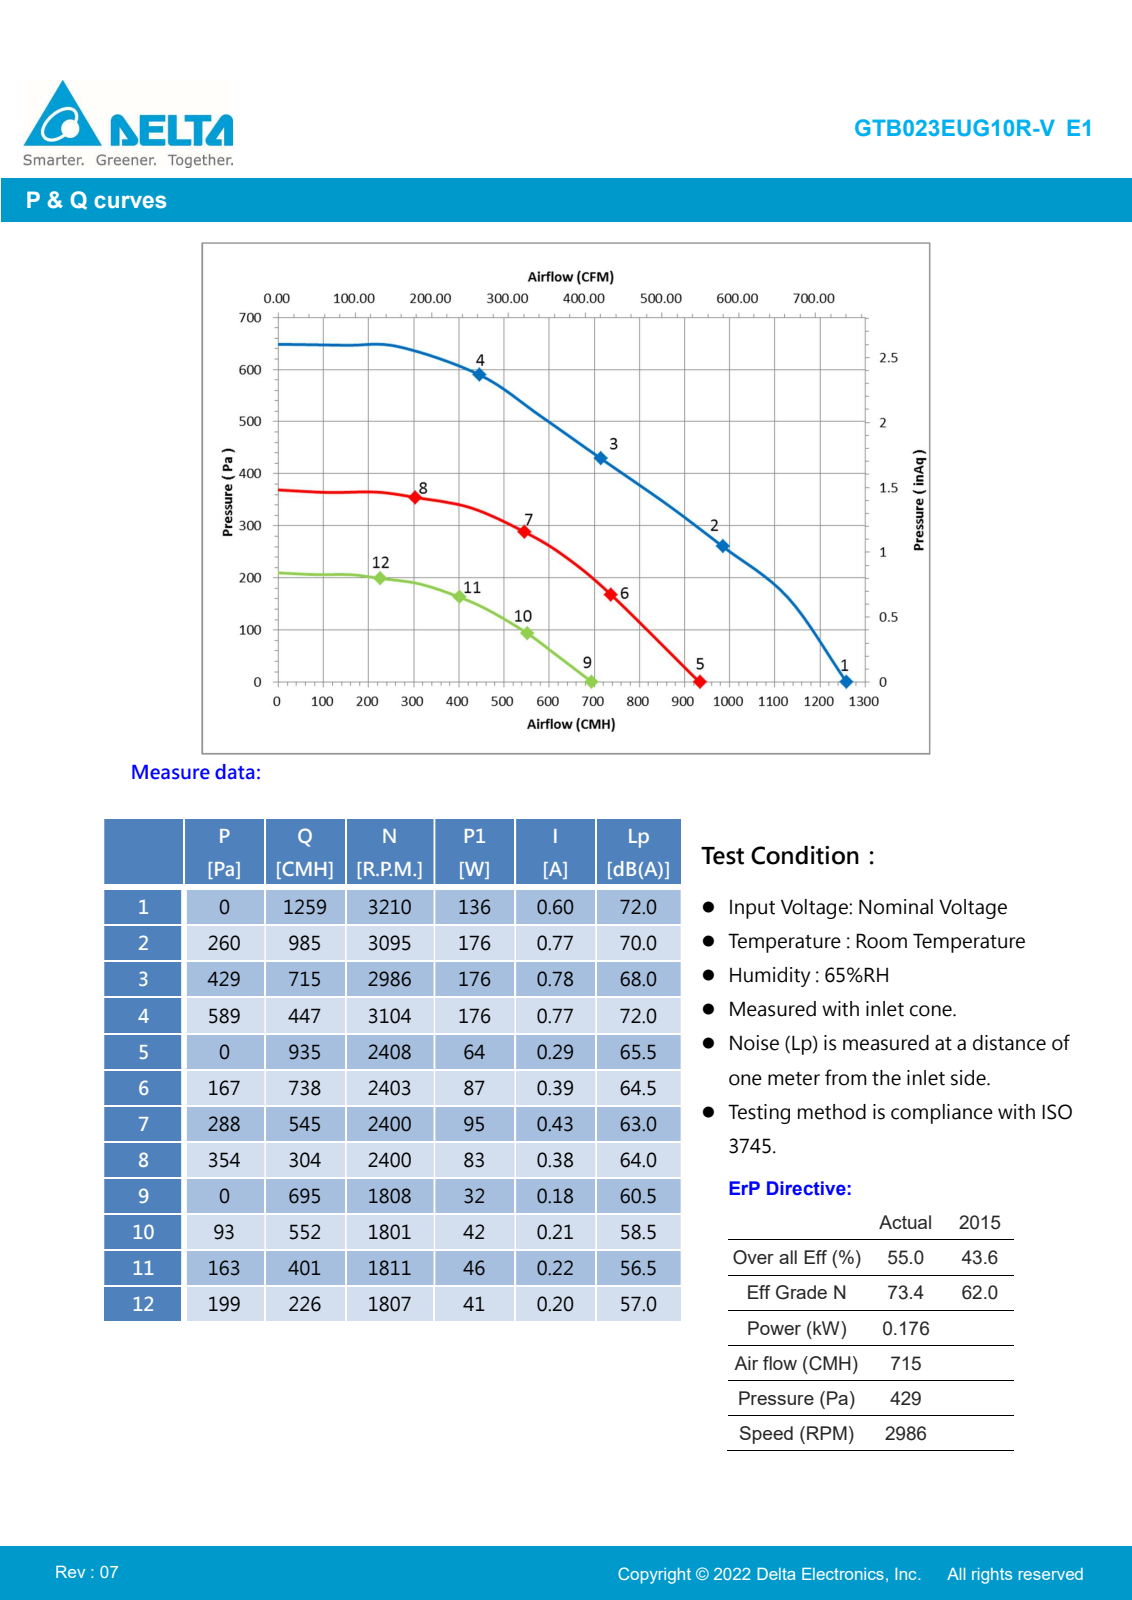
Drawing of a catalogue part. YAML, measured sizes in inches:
part_name: "OD55 Si-steel_all-(insert)_for BMC_170W BMC 部分; 防水墊片; M5 內六角_10; 防水蓋NN (+8 more)"
step_written_by: "SolidWorks 2020 (AUTOMOTIVE_DESIGN)"
units: inches
bodies: {solids: 23, faces: 2365, planar: 804, cylindrical: 532, other: 1029}
overall_size: [11.276, 11.267, 4.929]
volume: 123.8
surface_area: 532.9
round_holes:
  - {diameter: 0.236, count: 13}
  - {diameter: 0.098, count: 6}
  - {diameter: 0.13, count: 6}
  - {diameter: 0.197, count: 5}
  - {diameter: 0.165, count: 4}
  - {diameter: 0.177, count: 4}
  - {diameter: 0.094, count: 3}
  - {diameter: 0.157, count: 3}
  - {diameter: 0.213, count: 3}
  - {diameter: 0.291, count: 3}
  - {diameter: 0.362, count: 3}
  - {diameter: 0.083, count: 2}
round_bosses_or_shafts:
  - {diameter: 0.035, count: 7}
  - {diameter: 0.197, count: 5}
  - {diameter: 0.02, count: 4}
  - {diameter: 0.335, count: 3}
  - {diameter: 0.283, count: 3}
  - {diameter: 0.209, count: 3}
  - {diameter: 0.154, count: 3}
  - {diameter: 0.059, count: 3}
partial_cylinders:
  - {radius: 0.02, count: 116}
  - {radius: 0.008, count: 24}
  - {radius: 0.039, count: 24}
  - {radius: 0.016, count: 13}
  - {radius: 0.031, count: 11}
  - {radius: 0.157, count: 8}
  - {radius: 3.74, count: 7}
  - {radius: 3.819, count: 7}
face_to_face_distances: [0.059, 4.504, 4.445, 2.047, 2.398, 2.457, 2.296, 0.249, 2.149, 2.208]
hole_center_spacings: [2.108, 0.827, 1.142, 1.811, 2.913, 0.63, 1.41, 1.615]
